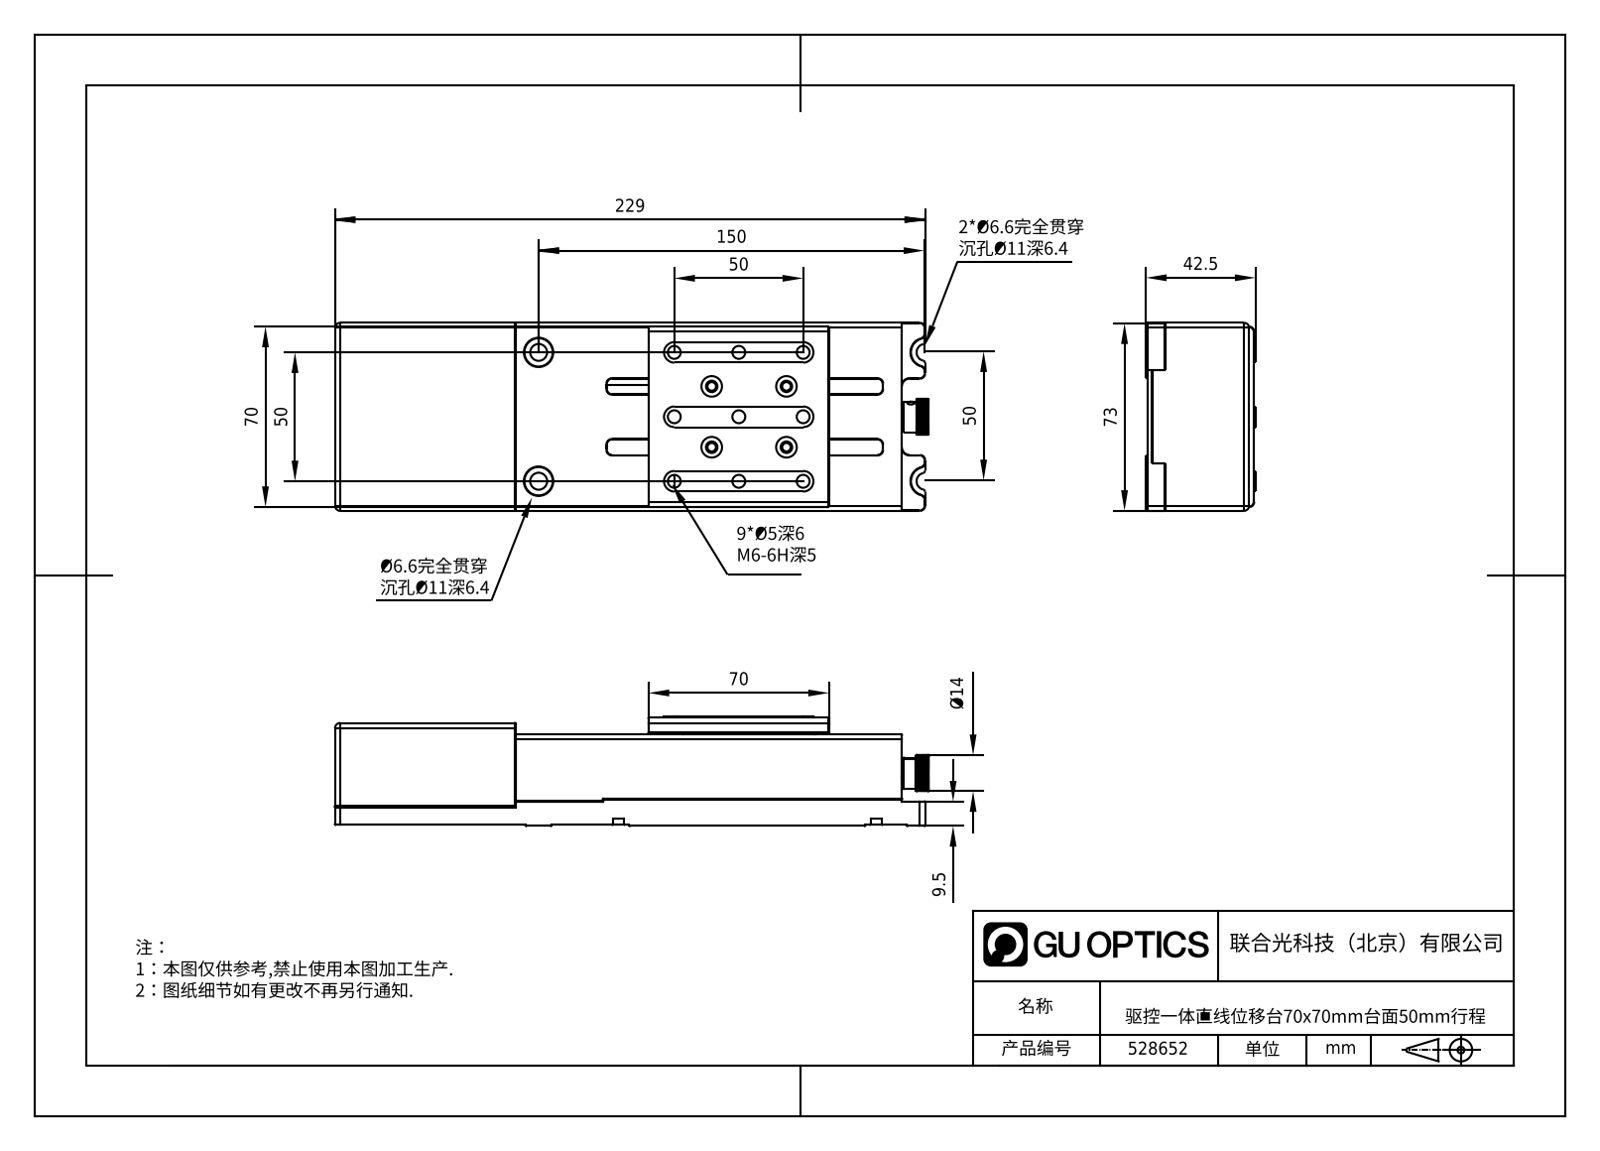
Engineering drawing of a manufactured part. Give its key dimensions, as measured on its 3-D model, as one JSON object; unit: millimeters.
{"part_name": "528652", "step_written_by": "SolidWorks 2020 (CONFIG_CONTROL_DESIGN)", "units": "millimeters", "bodies": {"solids": 45, "faces": 2496, "planar": 1311, "cylindrical": 712, "other": 473}, "overall_size": [230.5, 73, 42.5], "volume_mm3": 432296, "surface_area_mm2": 185023, "round_holes": [[2.4, 38], [1.6, 22], [4.4, 21], [2.5, 17], [1.57, 16], [3.4, 16], [4.2, 14], [6.5, 12], [5, 10], [3.3, 6], [1.57, 4], [2, 4]], "round_bosses_or_shafts": [[2.2, 4], [2, 4], [22, 1], [12, 1]], "partial_cylinders_radius": [[2, 31], [1, 25], [4, 6], [2.2, 5], [0.7, 4], [1.3, 4], [0.3, 2], [0.4, 2]], "face_to_face_distances": [2, 4, 33, 1, 35, 26, 2.5, 24, 7, 9], "hole_center_spacings": [9, 25, 47.6, 8, 12, 14.42, 18.26, 29.5]}
